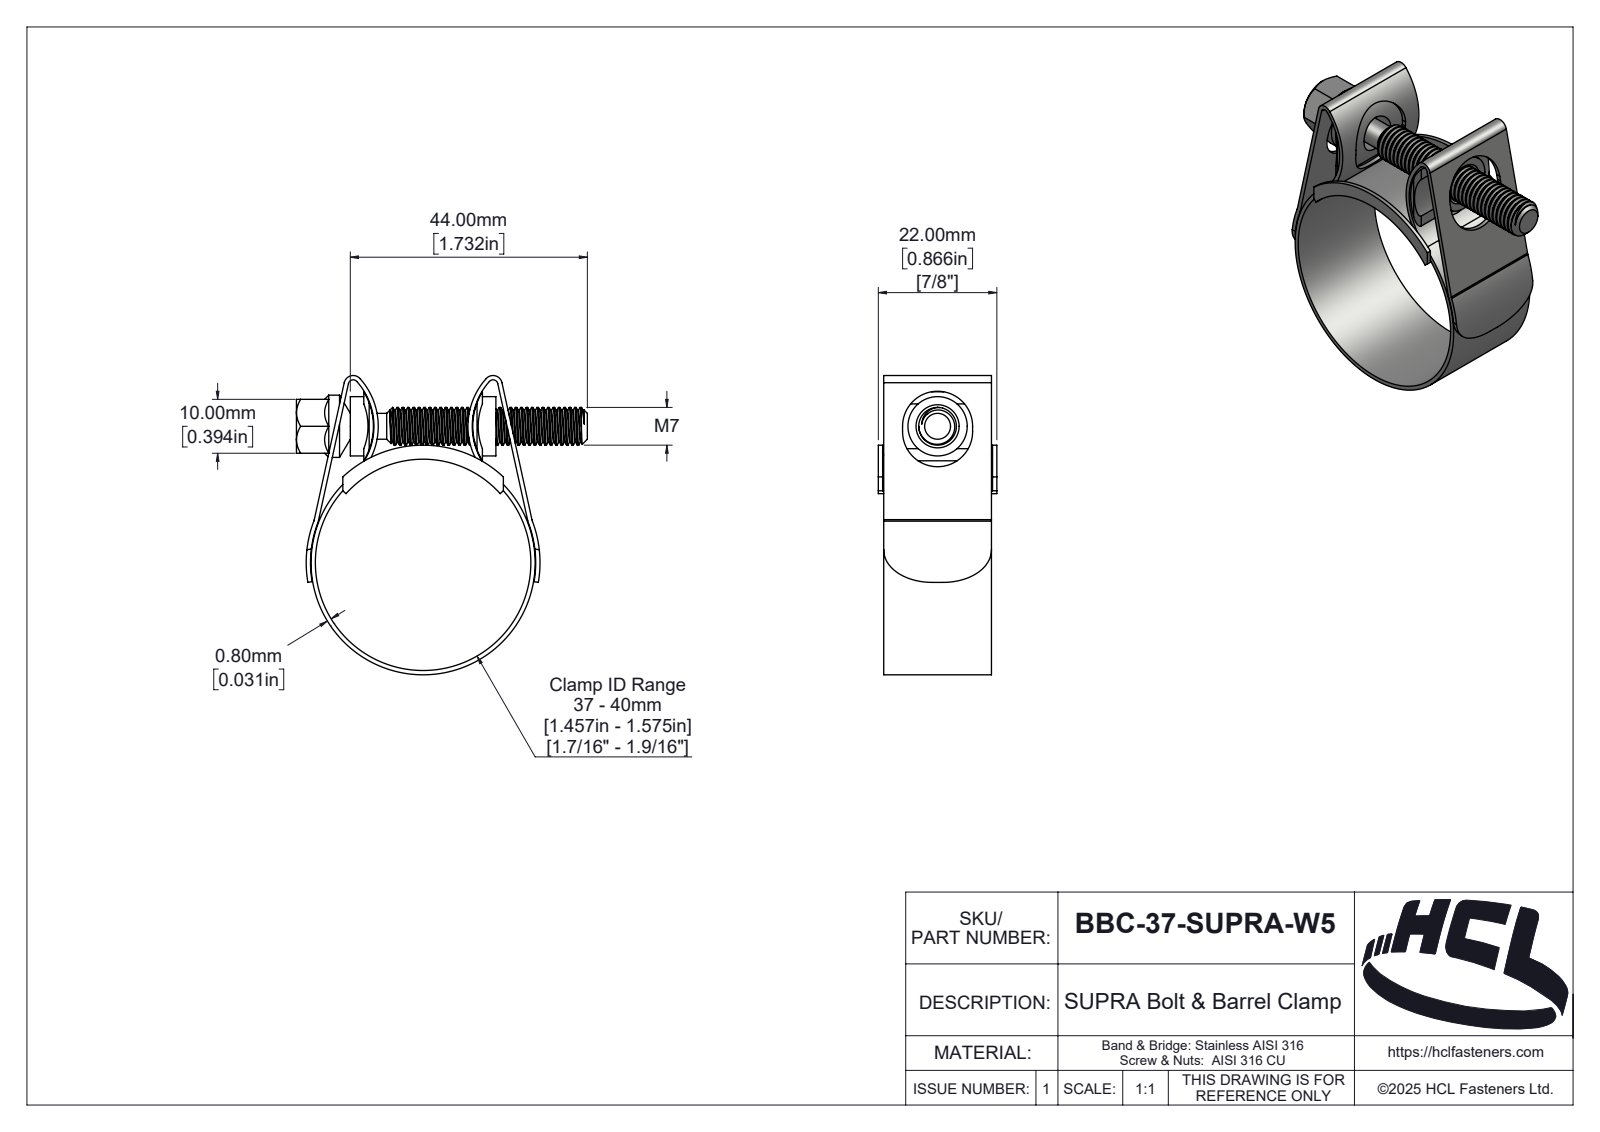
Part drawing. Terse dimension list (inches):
name: BBC-37-SUPRA-W5
written by: SolidWorks 2025 (AUTOMOTIVE_DESIGN)
unit: in
bodies: 5 solids, 309 faces (46 planar, 184 cylindrical, 79 other)
size: 2.186 × 2.126 × 0.866
volume: 0.401 in³; area: 20.07 in²
holes: 1× ⌀1.575
bosses: 1× ⌀0.455, 1× ⌀0.433, 1× ⌀0.276, 1× ⌀0.189
rounds: 4× R0.039, 2× R0.035, 2× R0.067, 2× R0.079, 2× R0.11, 2× R0.256, 2× R0.447, 2× R0.487
face distances: 0.031, 0.039, 0.827, 0.787, 0.394, 0.835, 0.795, 0.098, 0.965, 0.866
